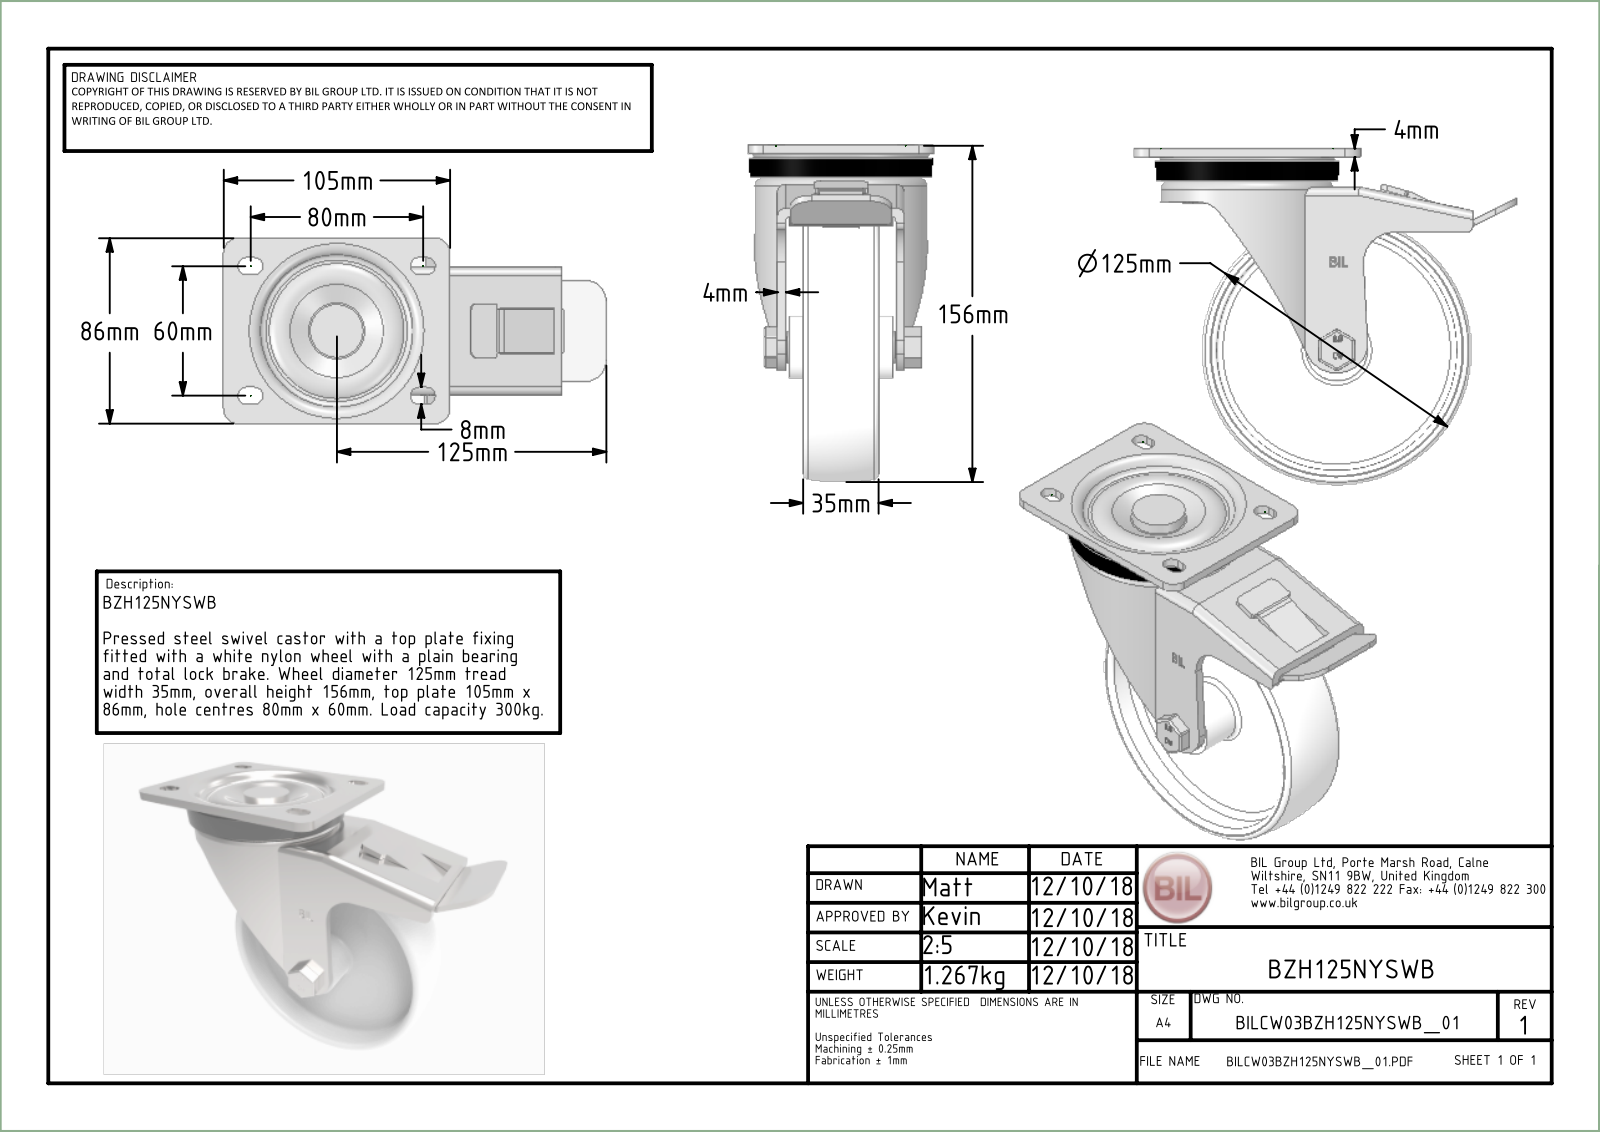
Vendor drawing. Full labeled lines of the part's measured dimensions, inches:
Part name (STEP PRODUCT): BZH125NYSWB v3; BZH125ASSWB v1; ZINC PLATED, PRESSED STEEL TOP PLATE; ZINC PLATED, PRESSED STEEL FORKS (+8 more)
STEP written by: Autodesk Translation Framework v14.10.0.0 (AUTOMOTIVE_DESIGN)
Units: inches
Bodies: 11 solids, 736 faces (411 planar, 176 cylindrical, 149 other)
Overall size (bounding box): 6.988 × 6.102 × 3.386
Volume: 21.48 in³ · Surface area: 228.8 in²
Round holes (diameter × count): ⌀0.236 ×1, ⌀0.394 ×1, ⌀0.402 ×1, ⌀0.413 ×1, ⌀0.472 ×1, ⌀0.594 ×1, ⌀0.984 ×1, ⌀1.26 ×1, ⌀2.835 ×1, ⌀4.409 ×1
Round bosses / shafts (diameter × count): ⌀3.15 ×1, ⌀2.441 ×1, ⌀2.362 ×1, ⌀1.22 ×1, ⌀1.142 ×1, ⌀0.787 ×1, ⌀0.63 ×1, ⌀0.591 ×1
Partial cylindrical surfaces — rounded edges, fillets, slot ends (radius × count): R0.02 ×19, R0.03 ×14, R0.059 ×8, R0.079 ×8, R0.177 ×8, R0.118 ×6, R0.157 ×4, R0.315 ×4
Main face-to-face distances: 0.157, 0.866, 0.276, 1.024, 1.299, 0.295, 1.142, 2.165, 0.138, 0.039
